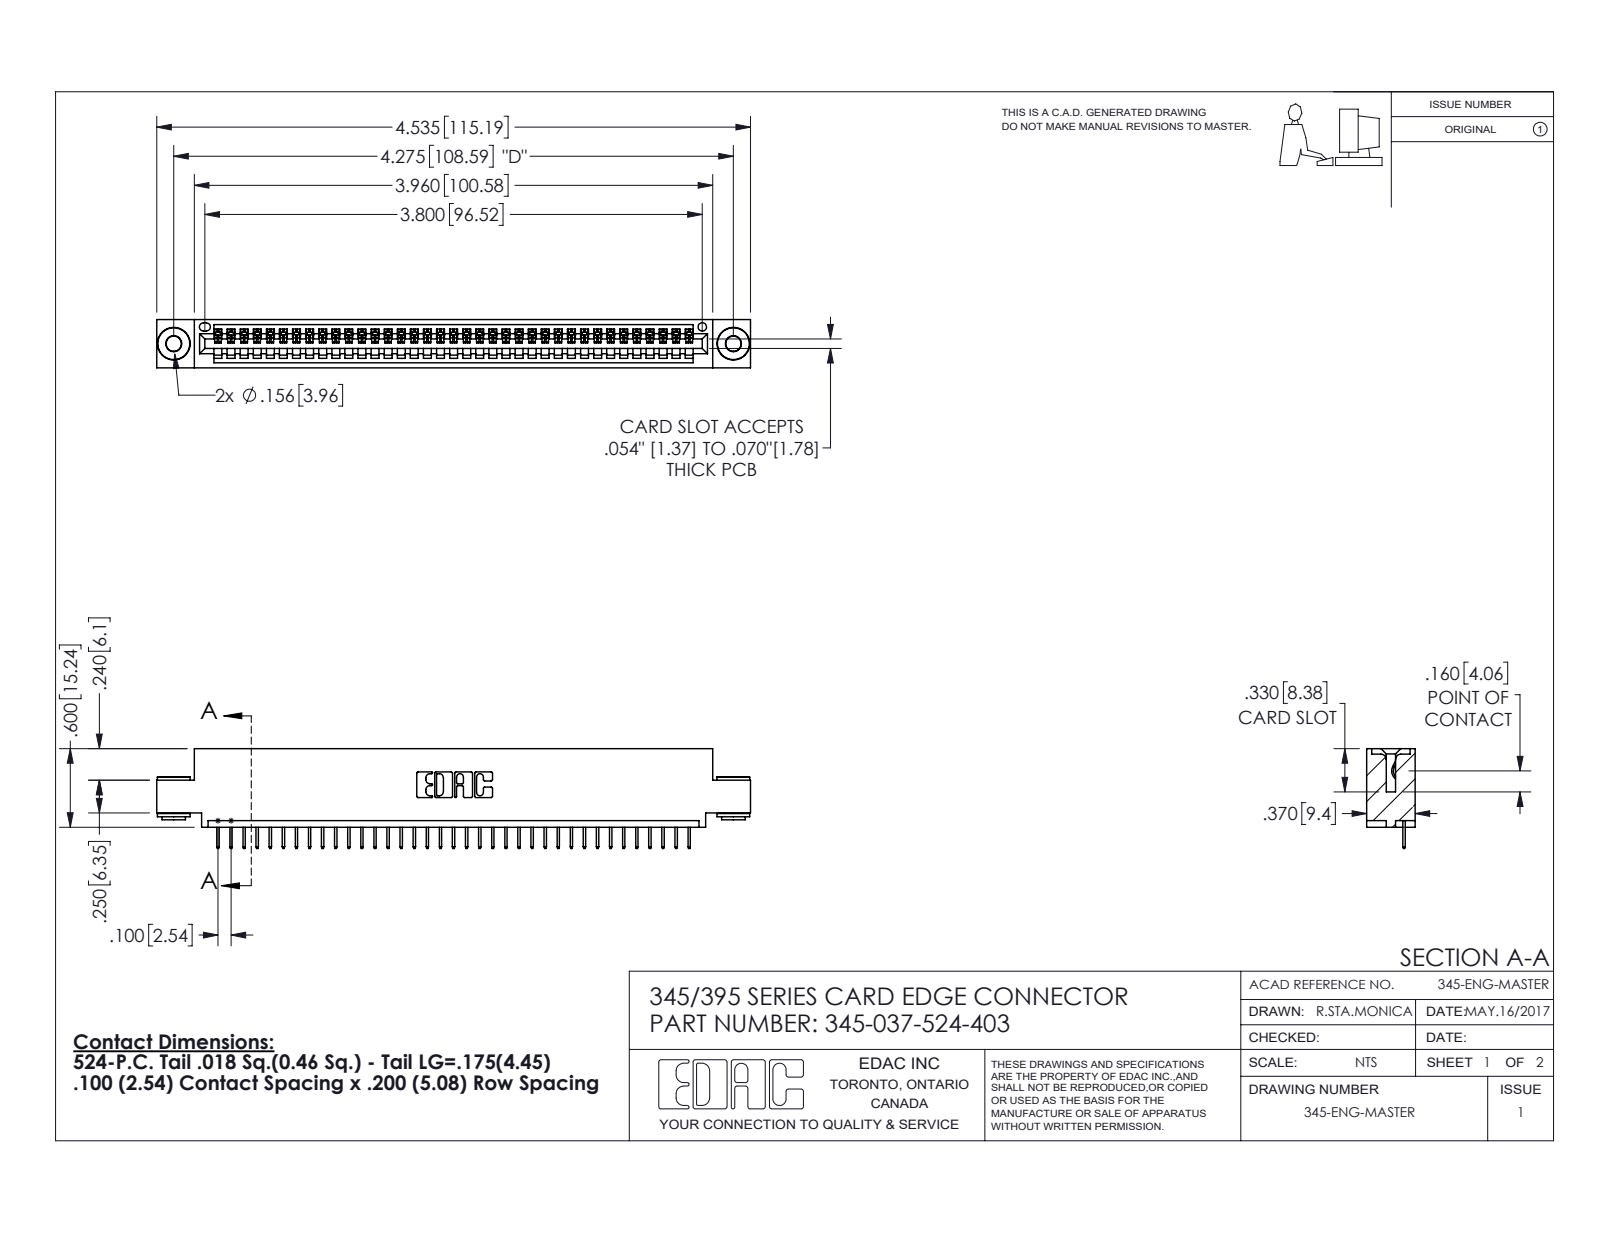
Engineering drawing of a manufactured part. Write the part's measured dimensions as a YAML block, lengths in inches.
part_name: "345-037-524-403; 345-250-002_345-250-002-102; 345-292-001_345-293-124; 345 Part_0.110 Offset - 0.156 Dia-TH"
step_written_by: "SolidWorks 2016 (CONFIG_CONTROL_DESIGN)"
units: inches
bodies: {solids: 40, faces: 2462, planar: 1796, cylindrical: 658, other: 8}
overall_size: [4.535, 0.762, 0.37]
volume: 0.653
surface_area: 21.67
round_holes:
  - {diameter: 0.116, count: 2}
  - {diameter: 0.156, count: 2}
  - {diameter: 0.064, count: 1}
round_bosses_or_shafts:
  - {diameter: 0.25, count: 2}
  - {diameter: 0.18, count: 2}
  - {diameter: 0.136, count: 2}
partial_cylinders:
  - {radius: 0.006, count: 74}
  - {radius: 0.01, count: 22}
  - {radius: 0.007, count: 6}
  - {radius: 0.031, count: 6}
  - {radius: 0.026, count: 3}
  - {radius: 0.031, count: 2}
  - {radius: 0.04, count: 2}
  - {radius: 0.014, count: 1}
face_to_face_distances: [0.072, 0.298, 0.37, 0.2, 0.025, 0.098, 0.272, 0.225, 0.072, 0.149]
hole_center_spacings: [0.27, 4.039, 4.275]
